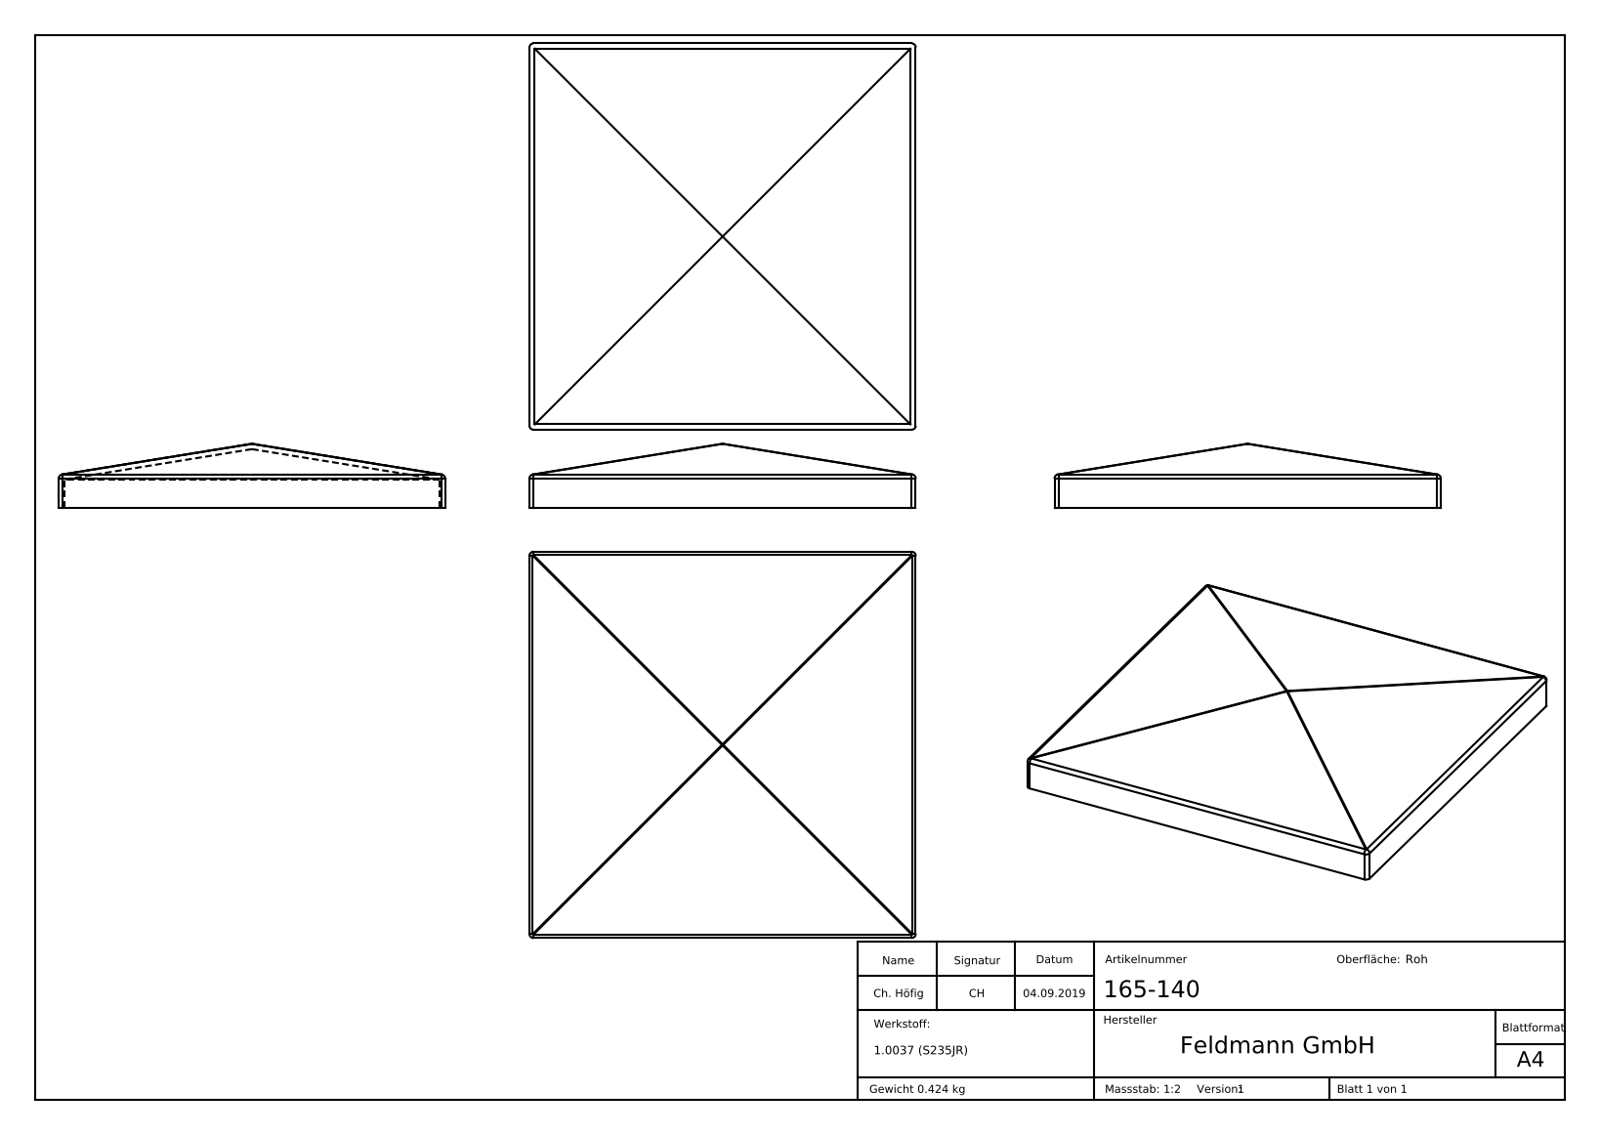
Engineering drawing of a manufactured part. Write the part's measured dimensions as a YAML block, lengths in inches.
part_name: "165-140"
step_written_by: "SolidWorks 2015 (CONFIG_CONTROL_DESIGN)"
units: inches
bodies: {solids: 1, faces: 224, planar: 130, cylindrical: 12, other: 82}
overall_size: [5.709, 5.709, 0.945]
volume: 3.313
surface_area: 85.85
partial_cylinders:
  - {radius: 0.059, count: 12}
face_to_face_distances: [0.079, 5.63, 5.709, 5.551, 0.075, 5.555, 5.634, 0.303, 0.447, 0.144]
